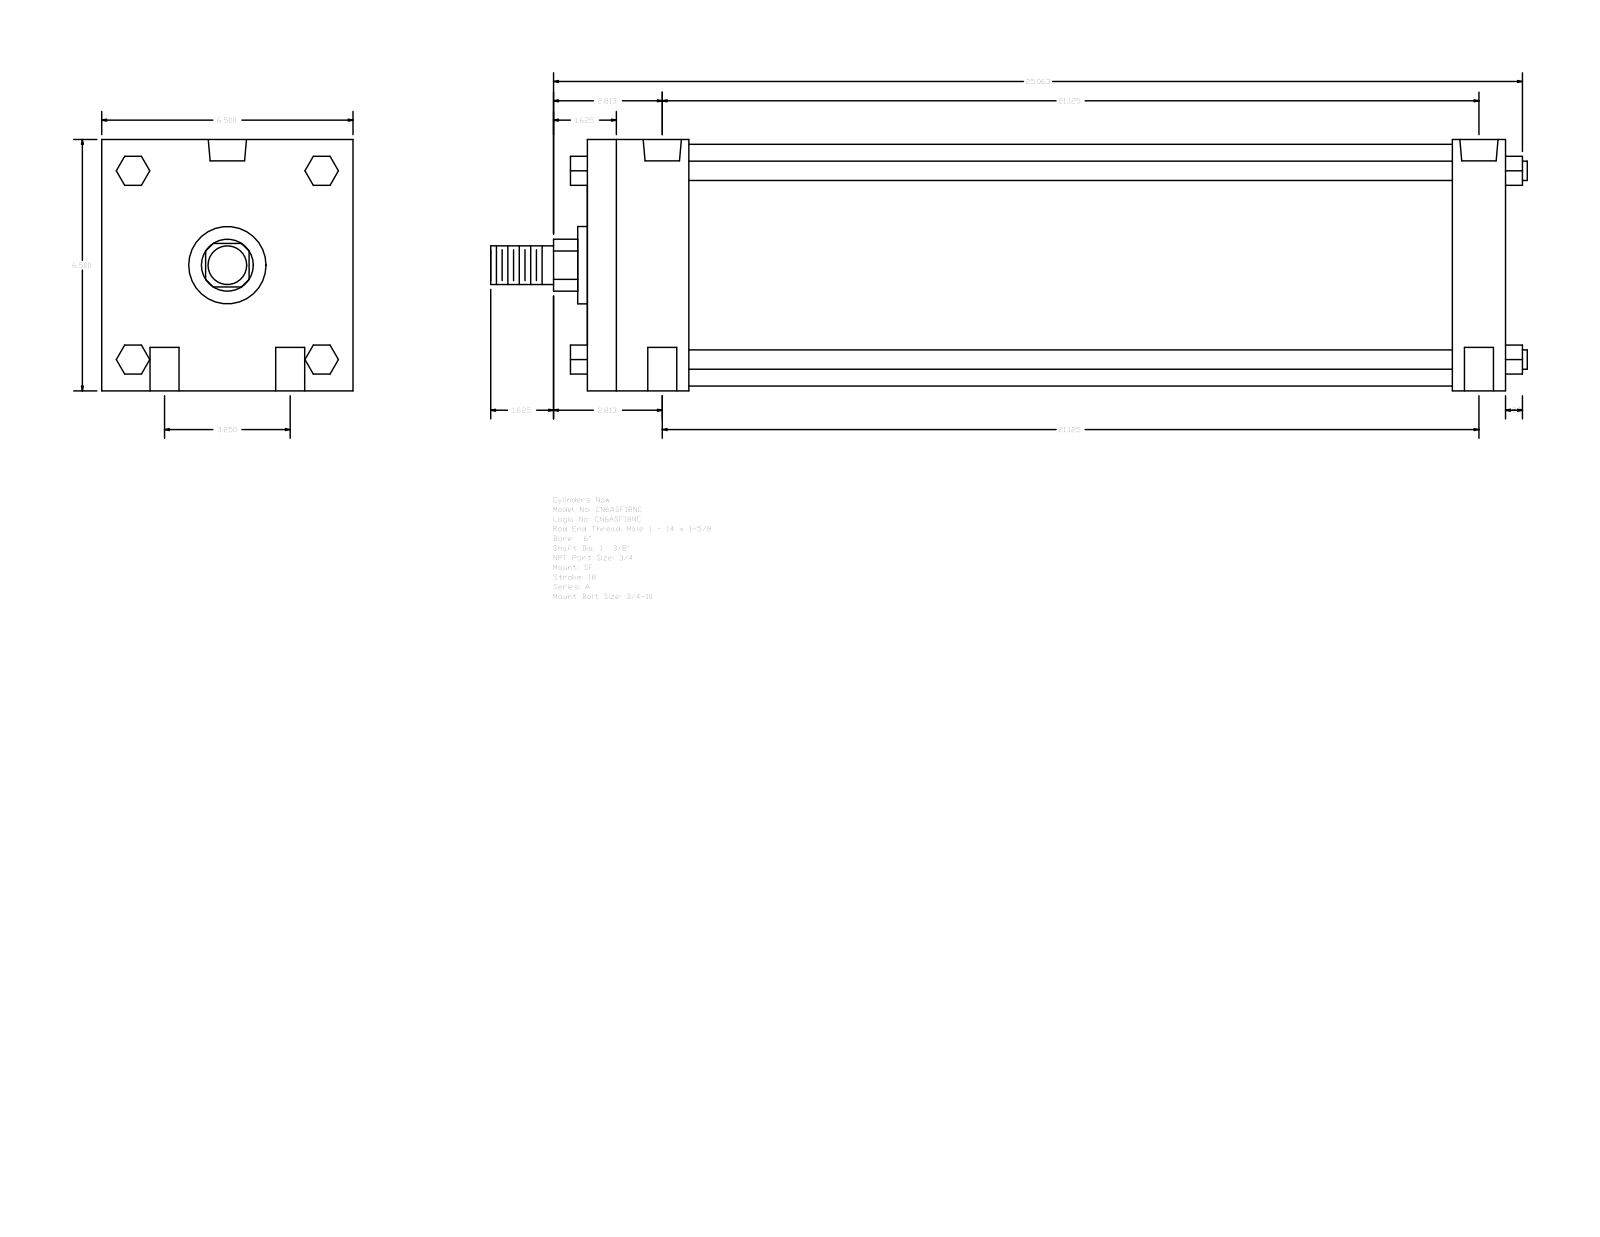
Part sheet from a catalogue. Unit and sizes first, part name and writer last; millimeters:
Units: millimetres
Overall size (bounding box): 681.04 × 165.1 × 165.1
Round holes (diameter × count): ⌀19.05 ×4, ⌀15.08 ×2, ⌀25.12 ×2
Round bosses / shafts (diameter × count): ⌀12.7 ×4, ⌀158.75 ×1, ⌀50.8 ×1, ⌀34.92 ×1, ⌀25.4 ×1
Partial cylindrical surfaces — rounded edges, fillets, slot ends (radius × count): R17.06 ×1
Main face-to-face distances: 165.1, 603.25, 568.32, 34.93, 66.67, 501.65, 536.58, 19.05, 61.97, 107.34
Hole centre spacings: 41.27, 538.15, 536.57, 82.54, 542.88, 525.45
Bodies: 0 solids, 124 faces (94 planar, 30 cylindrical, 0 other)
Part name (STEP PRODUCT): A_SF__0600_1.375
STEP written by: GSSL Pune (CONFIG_CONTROL_DESIGN)
